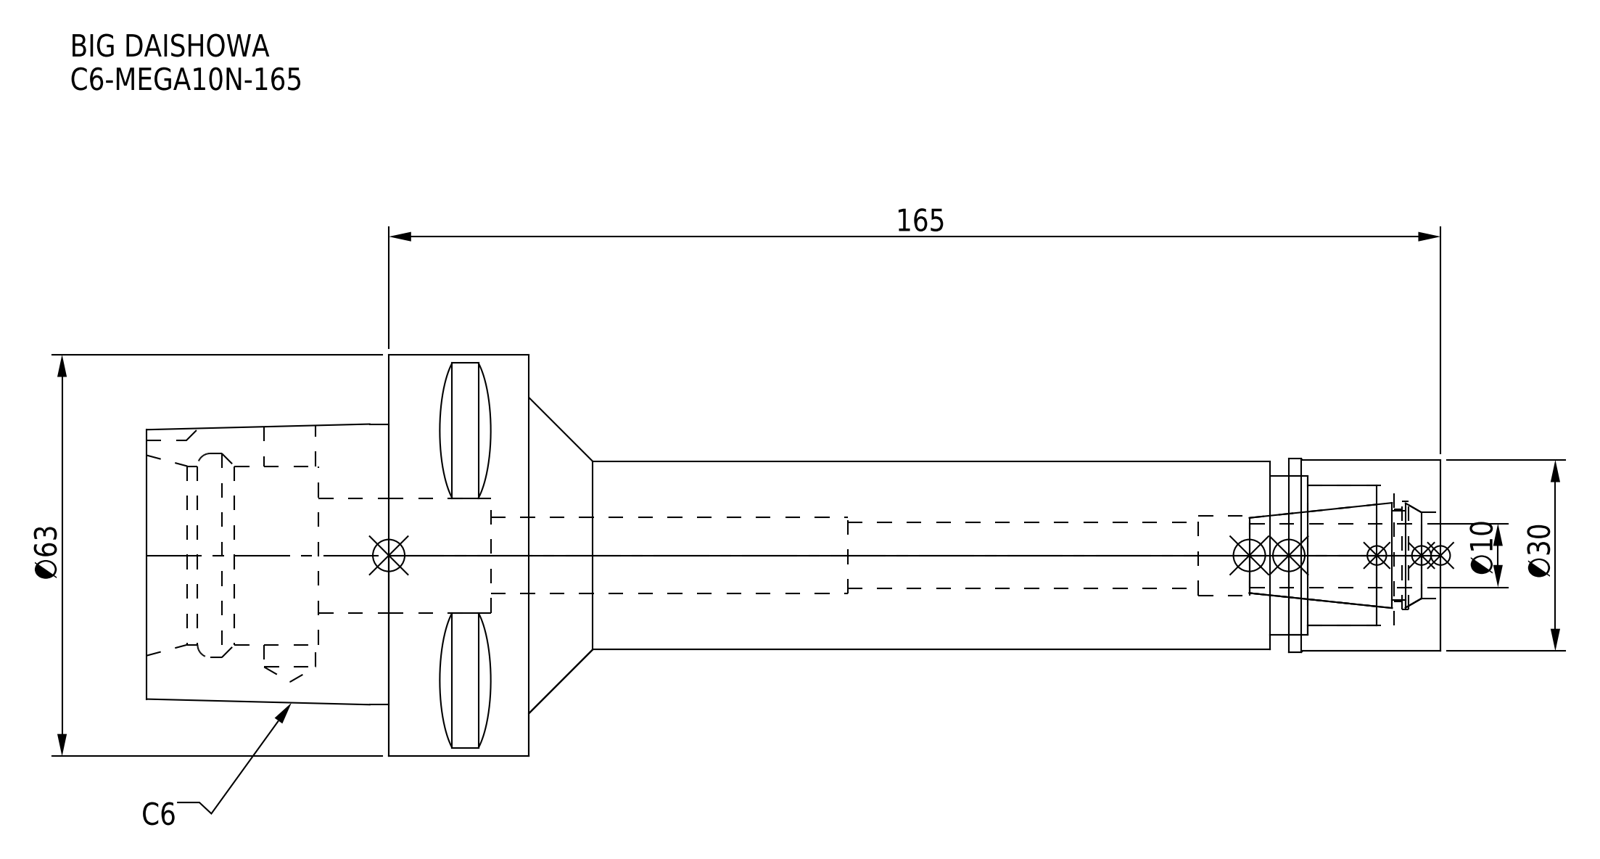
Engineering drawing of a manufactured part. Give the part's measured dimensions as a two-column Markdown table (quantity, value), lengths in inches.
| quantity | value |
| --- | --- |
| part name | C6-MEGA10N-165-100_ASM.stp; C6-MEGA10N-165-100.stp; C6-MEGA10N-165-100-FreeParts; DXF_TEMP_ASSY_ASM_4_ASM.stp (+3 more) |
| STEP written by | SolidWorks 2019 (CONFIG_CONTROL_DESIGN) |
| units | inches |
| bodies | 2 solids, 98 faces (39 planar, 41 cylindrical, 18 other) |
| overall size | 7.992 × 2.48 × 2.48 |
| volume | 11.15 in³ |
| surface area | 64.41 in² |
| round holes (diameter × count) | 0.319 × 1, 0.409 × 1, 0.472 × 1, 0.492 × 1, 0.531 × 1, 0.571 × 1, 0.669 × 1, 0.709 × 1, 0.866 × 1, 0.984 × 1, 1.102 × 1, 1.26 × 1 |
| round bosses / shafts (diameter × count) | 2.48 × 1, 1.193 × 1, 1.181 × 1, 1.161 × 1 |
| partial cylindrical surfaces (radius × count) | 0.197 × 1 |
| main face-to-face distances | 0.866, 5.63, 6.496, 1.496, 1.063, 7.992, 2.362, 1.299, 6.929, 0.433 |
